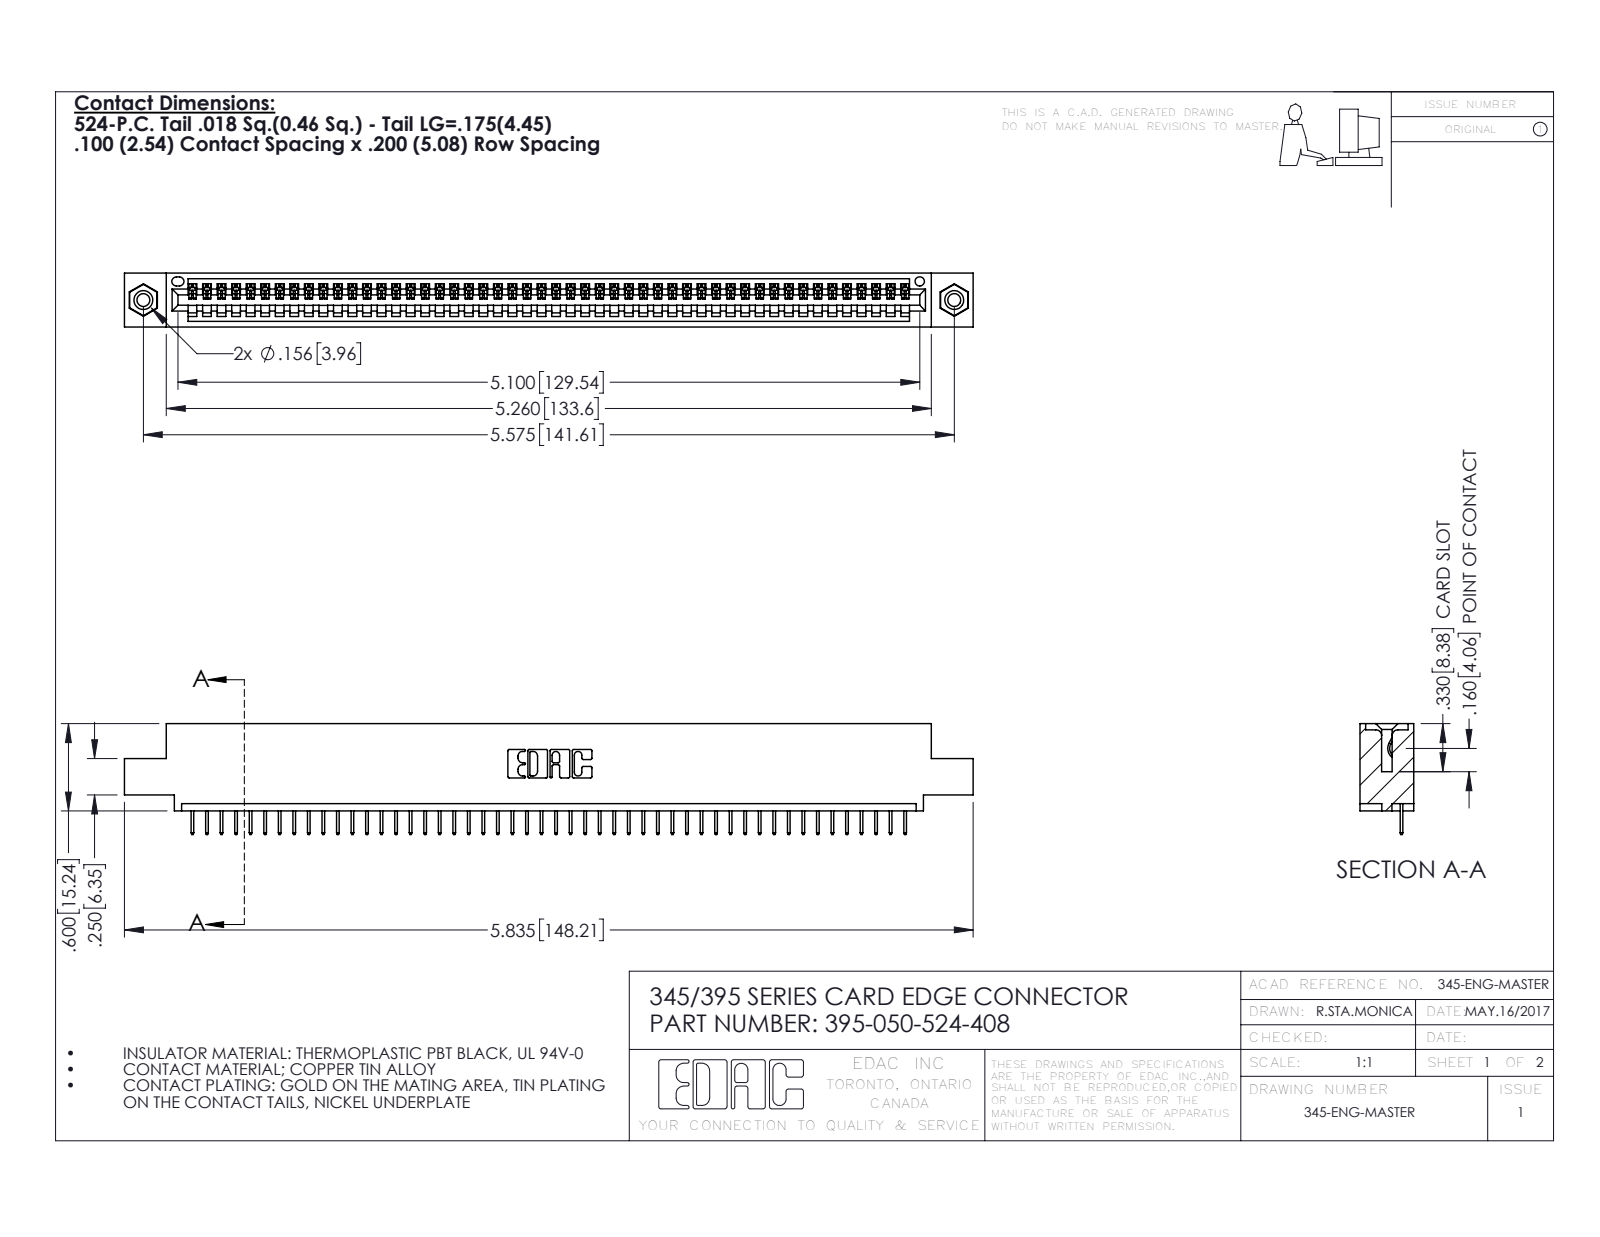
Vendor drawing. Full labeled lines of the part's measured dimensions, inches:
Part name (STEP PRODUCT): 345 Part_0.110 Offset - 0.156 Dia-TI; 345-250-001_345-250-003-102; 345-292-001_345-293-124; 395-050-524-408
STEP written by: SolidWorks 2016 (CONFIG_CONTROL_DESIGN)
Units: inches
Bodies: 53 solids, 3290 faces (2416 planar, 858 cylindrical, 16 other)
Overall size (bounding box): 5.835 × 0.762 × 0.37
Volume: 0.846 in³ · Surface area: 27.91 in²
Round holes (diameter × count): ⌀0.089 ×2, ⌀0.125 ×2, ⌀0.156 ×2, ⌀0.064 ×1
Round bosses / shafts (diameter × count): ⌀0.155 ×2
Partial cylindrical surfaces — rounded edges, fillets, slot ends (radius × count): R0.006 ×100, R0.01 ×22, R0.007 ×6, R0.031 ×6, R0.026 ×3, R0.031 ×2, R0.04 ×2, R0.014 ×1
Main face-to-face distances: 0.072, 0.298, 0.37, 0.2, 0.098, 0.272, 0.025, 0.225, 0.072, 0.149
Hole centre spacings: 0.27, 5.339, 5.575
